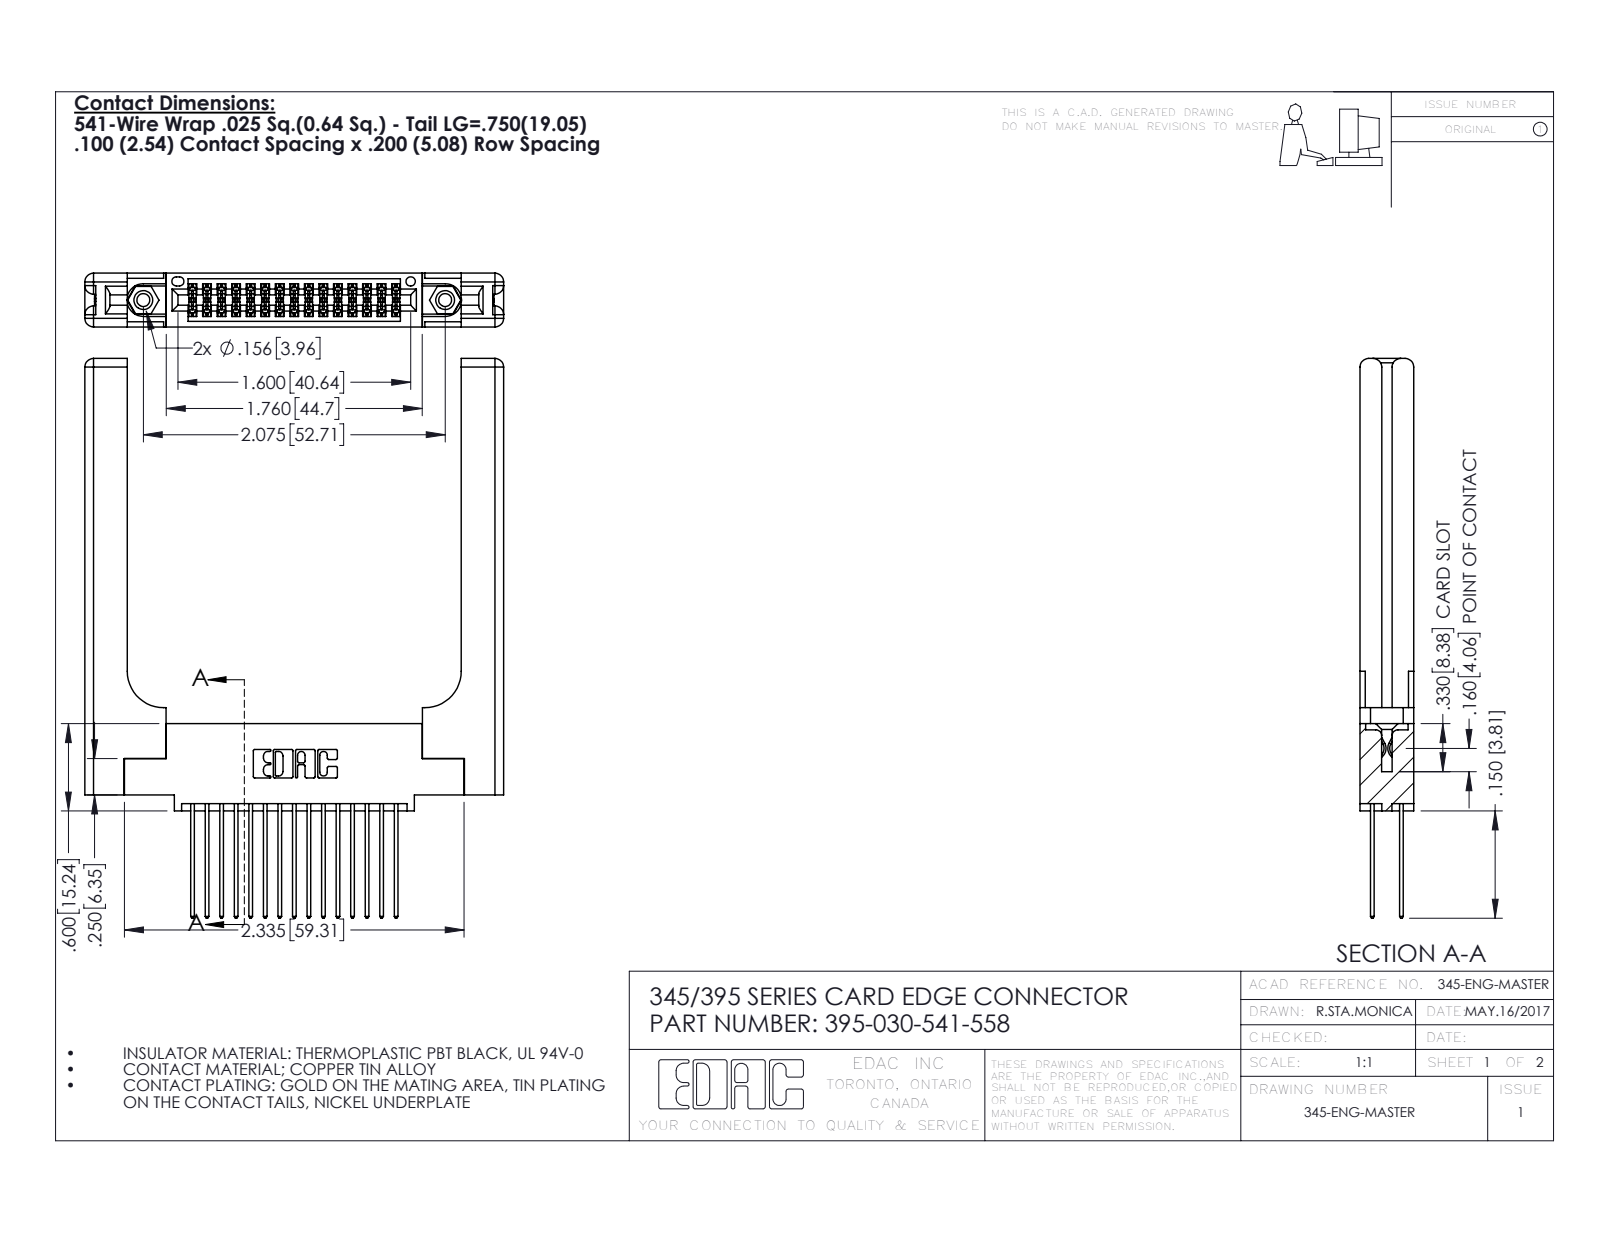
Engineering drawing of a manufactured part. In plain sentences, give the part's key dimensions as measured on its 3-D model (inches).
The part is named "345 Part_0.110 Offset - 0.156 Dia-TH; 395-030-541-558; 345-292-001_345-293-141; 345-250-001_345-250-001-102 (+1 more)". Its 3-D file was written by "SolidWorks 2016 (CONFIG_CONTROL_DESIGN)". It is 35 solids with 1886 faces: 1222 planar, 604 cylindrical and 60 other. Overall it measures 3.847 by 2.879 by 0.37 inches. Its volume is 0.941 cubic inches and its surface area 24.36 square inches. Round holes: 2 of diameter 0.089, 2 of diameter 0.125, 2 of diameter 0.156, 1 of diameter 0.064. Round bosses or shafts: 2 of diameter 0.155. Partial cylindrical surfaces (rounded edges, fillets, slot ends): 45 of radius 0.006, 30 of radius 0.01, 22 of radius 0.01, 16 of radius 0.06, 6 of radius 0.007, 6 of radius 0.031, 3 of radius 0.026, 2 of radius 0.014. The main face-to-face distances are 0.37, 0.072, 0.298, 0.098, 0.272, 0.025, 0.2, 0.148, 0.15, 0.077. The hole center spacings are 0.27, 1.842, 2.075.
